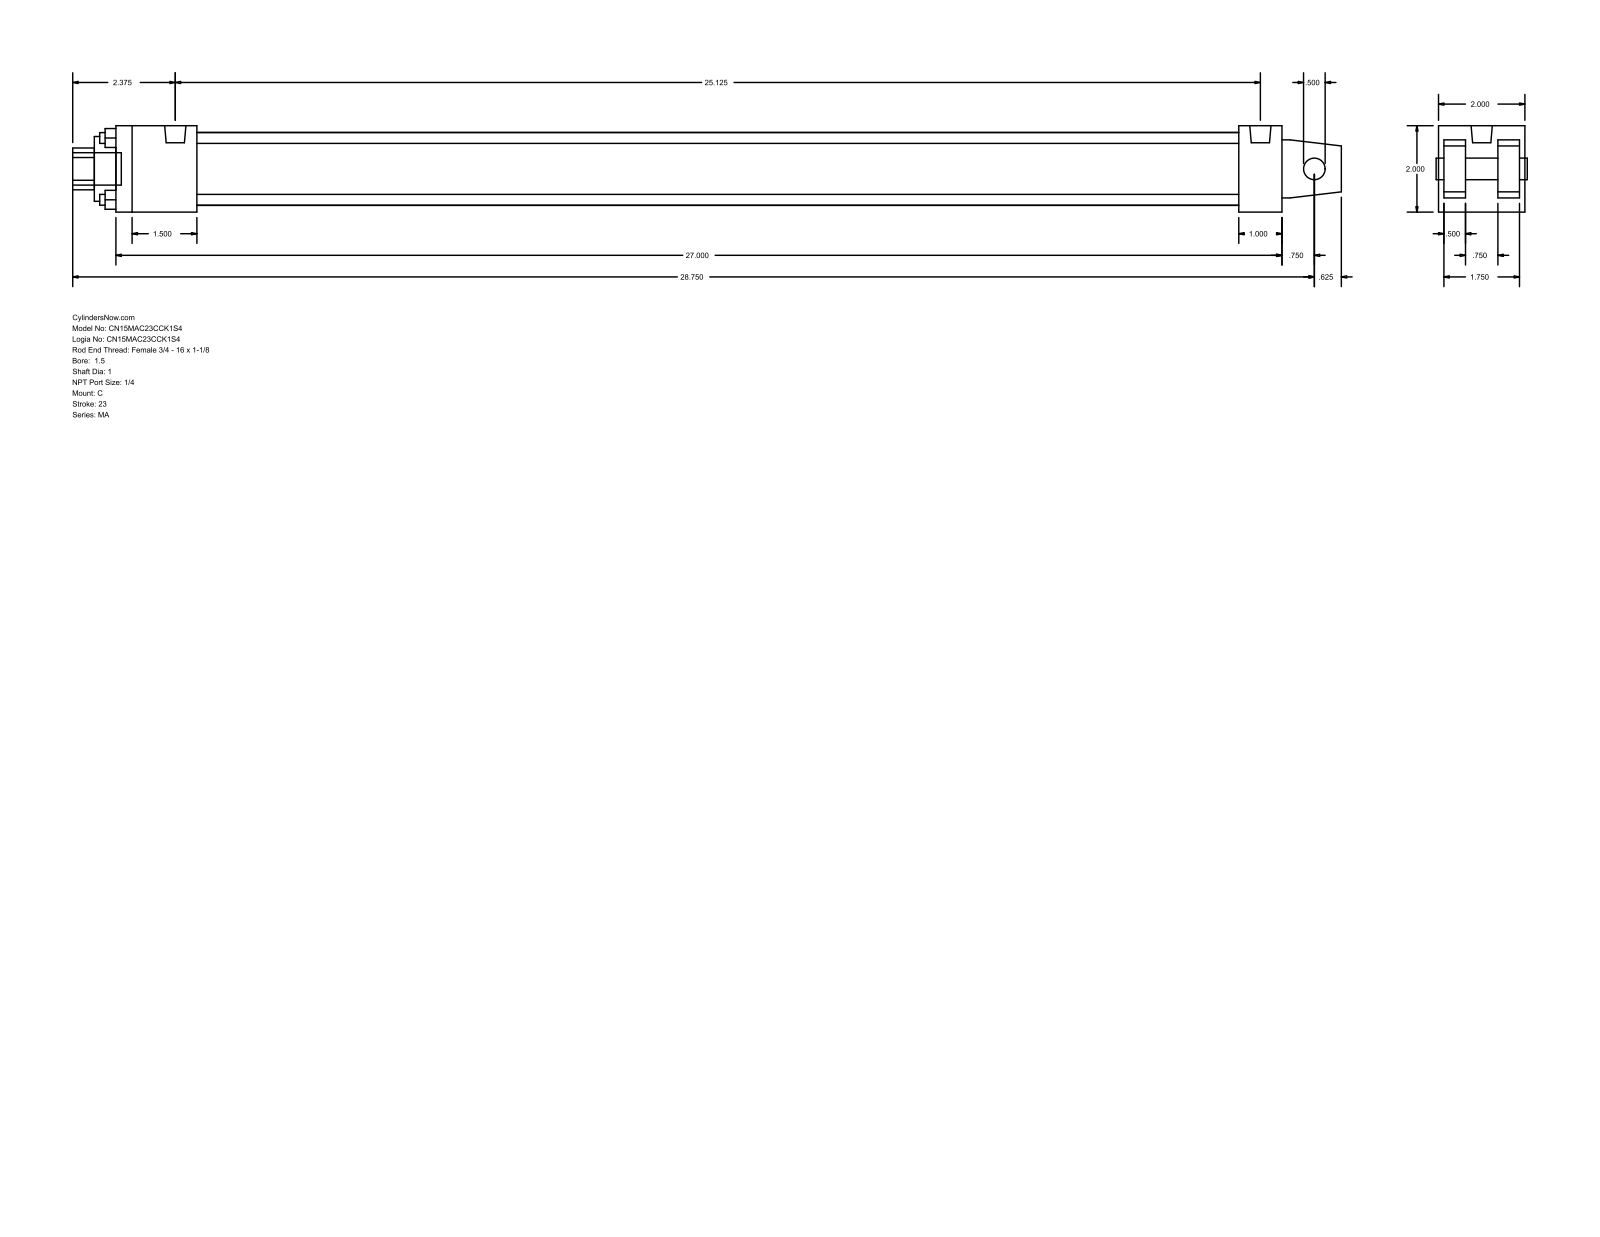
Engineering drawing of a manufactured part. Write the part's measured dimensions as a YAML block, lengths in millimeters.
part_name: "MA_C__0150_1"
step_written_by: "GSSL Pune (CONFIG_CONTROL_DESIGN)"
units: millimeters
bodies: {solids: 0, faces: 103, planar: 76, cylindrical: 27, other: 0}
overall_size: [746.12, 50.8, 50.8]
round_holes:
  - {diameter: 6.35, count: 4}
  - {diameter: 12.7, count: 1}
  - {diameter: 25.4, count: 1}
  - {diameter: 38.1, count: 1}
  - {diameter: 42.93, count: 1}
round_bosses_or_shafts:
  - {diameter: 7.94, count: 4}
  - {diameter: 12.49, count: 2}
  - {diameter: 19.05, count: 1}
partial_cylinders:
  - {radius: 12.29, count: 1}
face_to_face_distances: [50.8, 47.63, 12.7, 3.17, 15.87, 34.93, 31.76, 44.46, 685.8, 25.4]
hole_center_spacings: [25.68, 36.32, 51.36]
